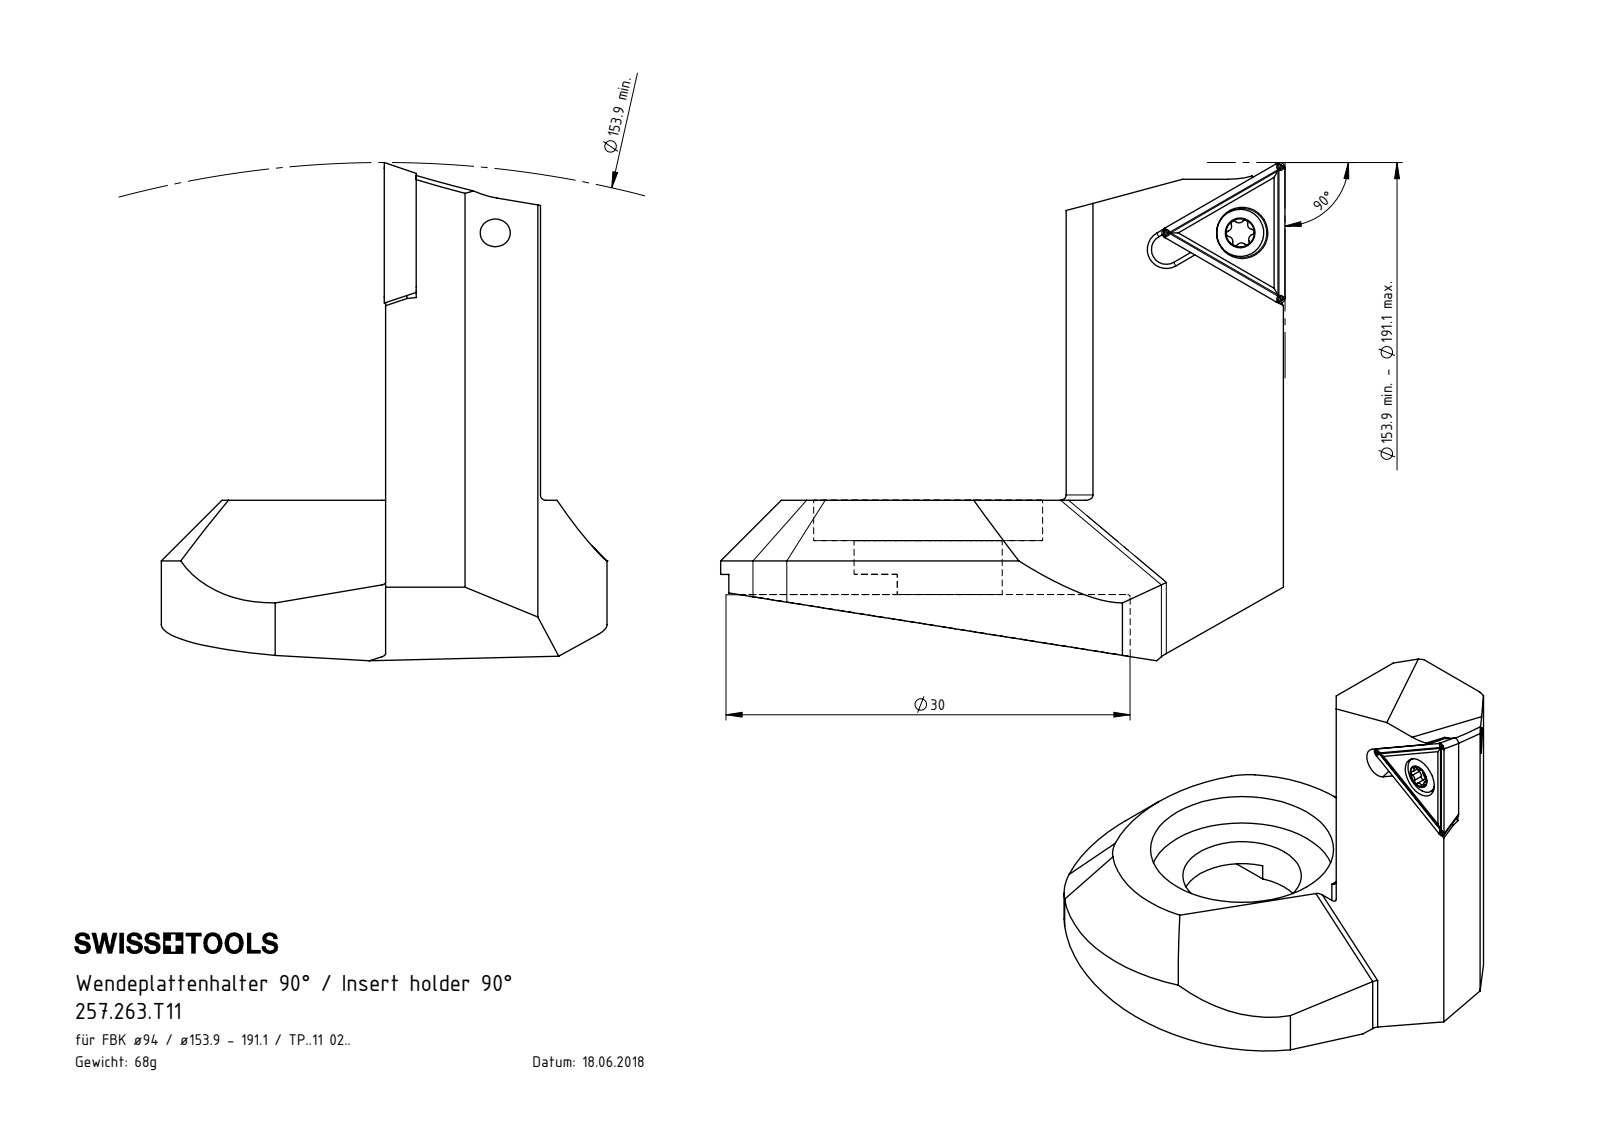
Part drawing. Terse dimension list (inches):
name: AV6-WTM.001.032_A_fertigbearbeitet; 257.263.T11; WTM-ER2.001.005_A; TPMT110204
written by: SolidWorks 2022 (AUTOMOTIVE_DESIGN)
unit: in
bodies: 3 solids, 171 faces (57 planar, 59 cylindrical, 55 other)
size: 1.65 × 1.456 × 1.303
volume: 0.532 in³; area: 6.874 in²
holes: 1× ⌀0.081, 1× ⌀0.11, 1× ⌀0.15, 1× ⌀0.433, 1× ⌀0.669, 1× ⌀1.181
bosses: 1× ⌀0.138, 1× ⌀0.098
rounds: 9× R0.016, 6× R0.008, 5× R0.014, 3× R0.008, 2× R0.394, 1× R0.014, 1× R0.043, 1× R0.276
face distances: 0.276, 0.453, 0.118, 0.157, 0.217, 0.098, 0.059, 0.363, 0.09, 0.197
